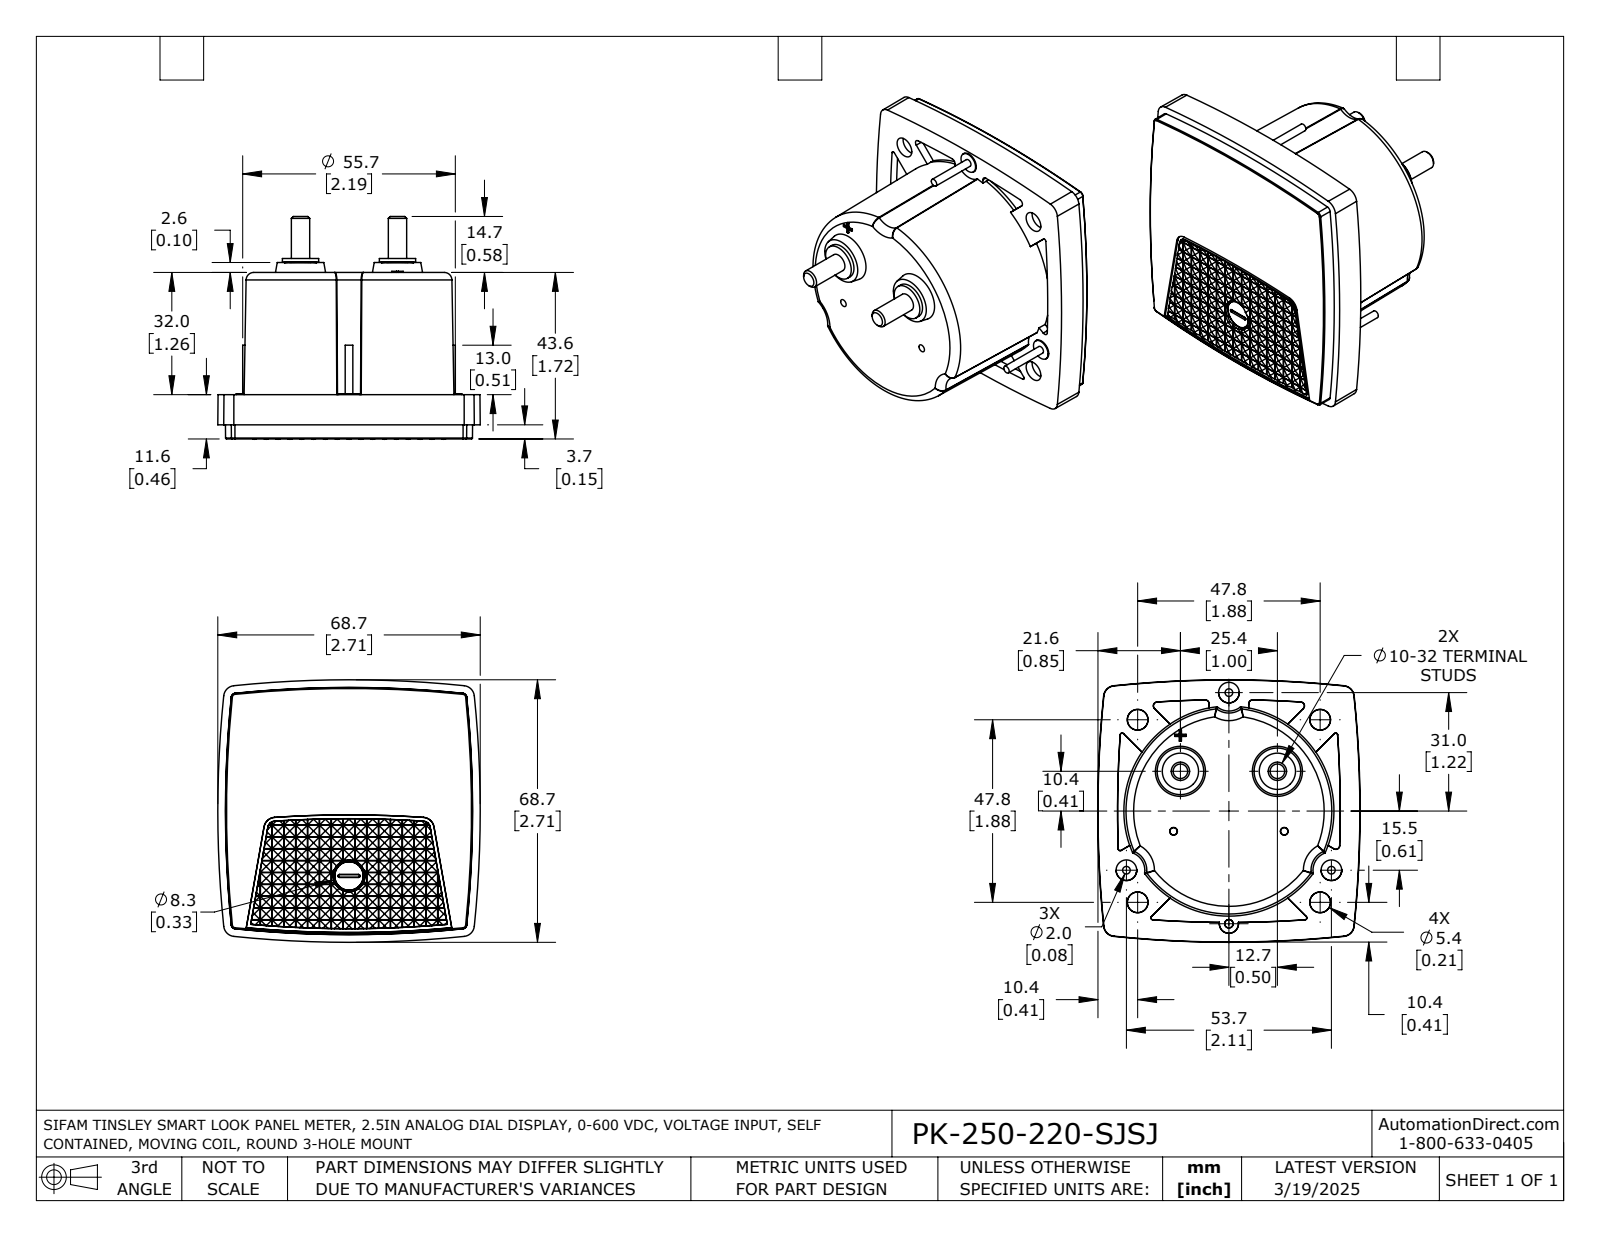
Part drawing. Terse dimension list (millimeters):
name: PK-250-220-SJSJ
written by: SolidWorks 2021 (AUTOMOTIVE_DESIGN)
unit: mm
bodies: 1 solid, 1550 faces (1165 planar, 265 cylindrical, 120 other)
size: 68.7 × 68.7 × 58.3
volume: 124 400 mm³; area: 19 620 mm²
bosses: 3× ⌀5.4, 3× ⌀2, 2× ⌀9.5, 2× ⌀4.8, 1× ⌀5.5
rounds: 2× R4.2, 1× R27.5
face distances: 43.6, 32, 11.6, 0.6, 2.2, 2.4, 7.9, 3, 1.8, 34.2
